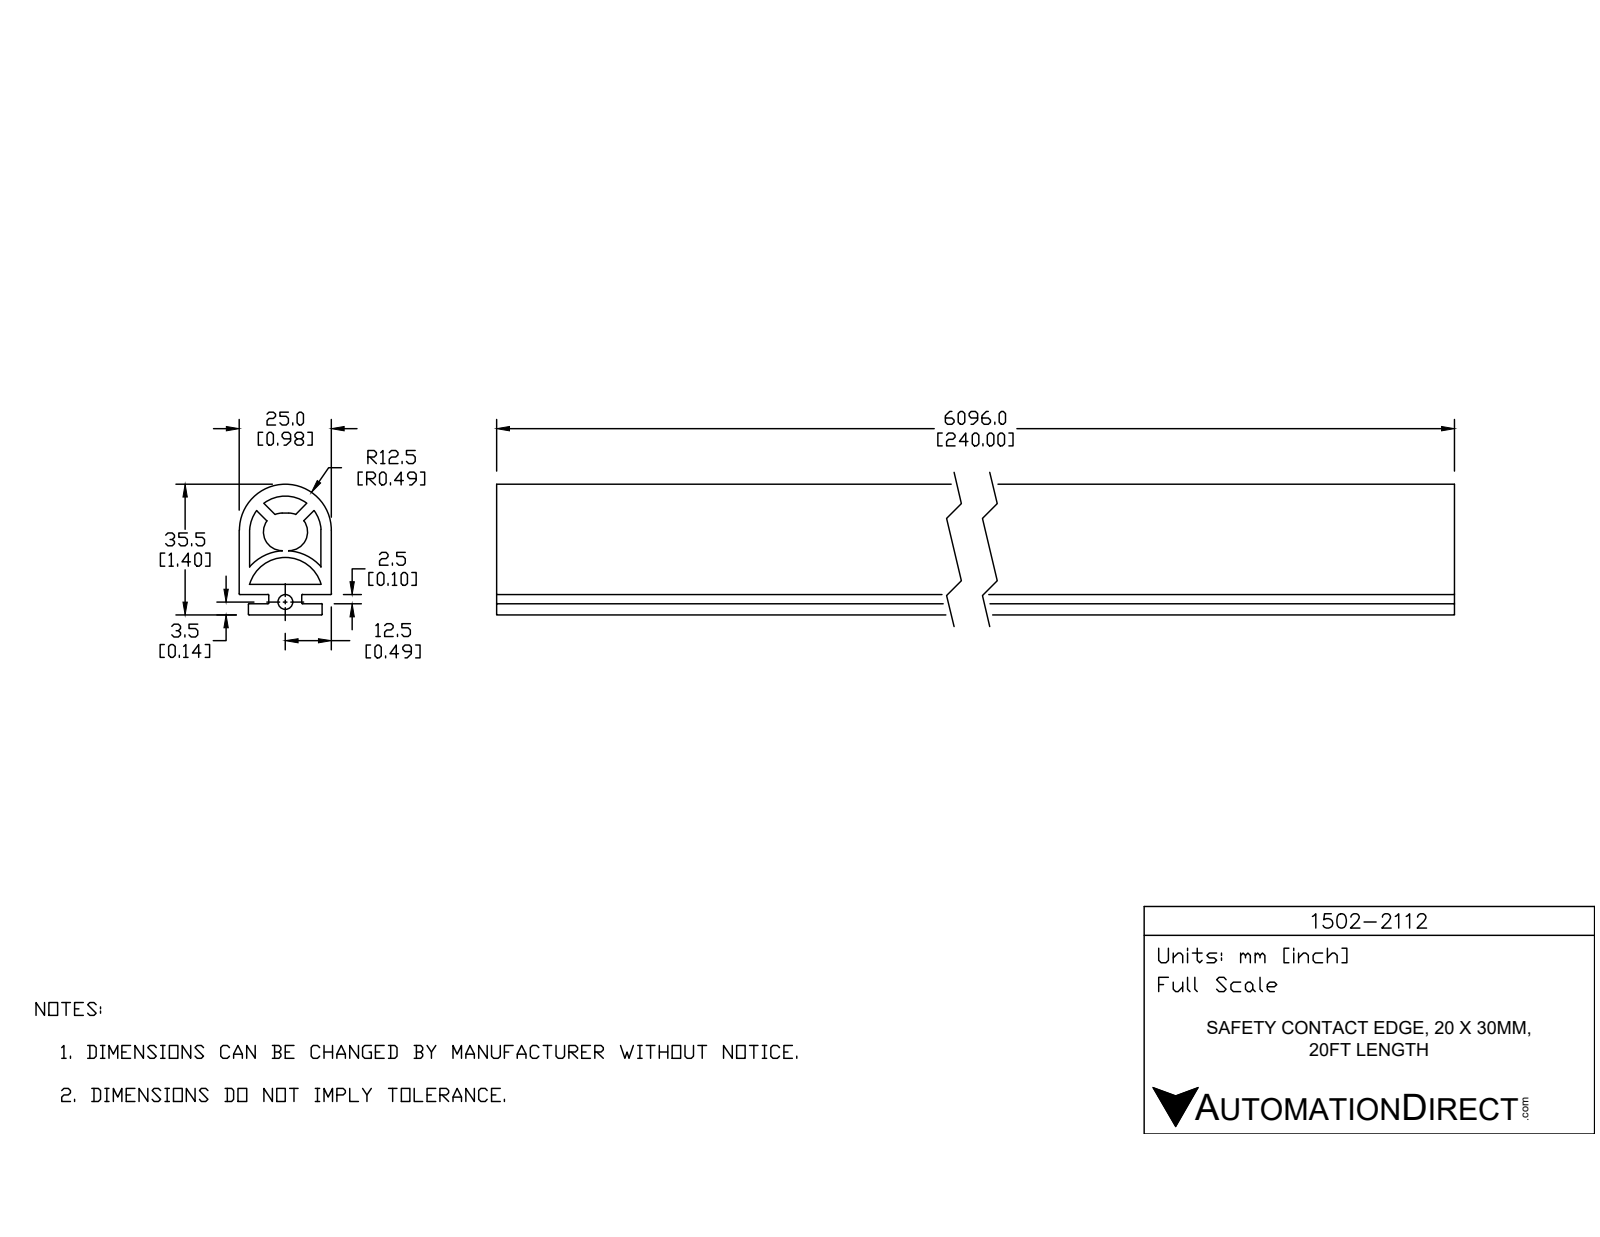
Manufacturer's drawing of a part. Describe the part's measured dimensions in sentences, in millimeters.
The part is named "1502-2112". Its 3-D file was written by "SolidWorks 2017 (AUTOMOTIVE_DESIGN)". It is 1 solid with 47 faces: 23 planar, 24 cylindrical and 0 other. Overall it measures 609.6 by 35.5 by 25 millimeters. Its volume is 304 311 cubic millimeters and its surface area 182 651 square millimeters. Round holes: 1 of diameter 4. Partial cylindrical surfaces (rounded edges, fillets, slot ends): 10 of radius 0.2, 2 of radius 5.12, 1 of radius 9.7, 1 of radius 10.11, 1 of radius 12.5, 1 of radius 12.9. The main face-to-face distances are 2.8, 5.5, 8.3, 25, 2.5, 3, 5.3, 2.85, 22.15, 22.2.
